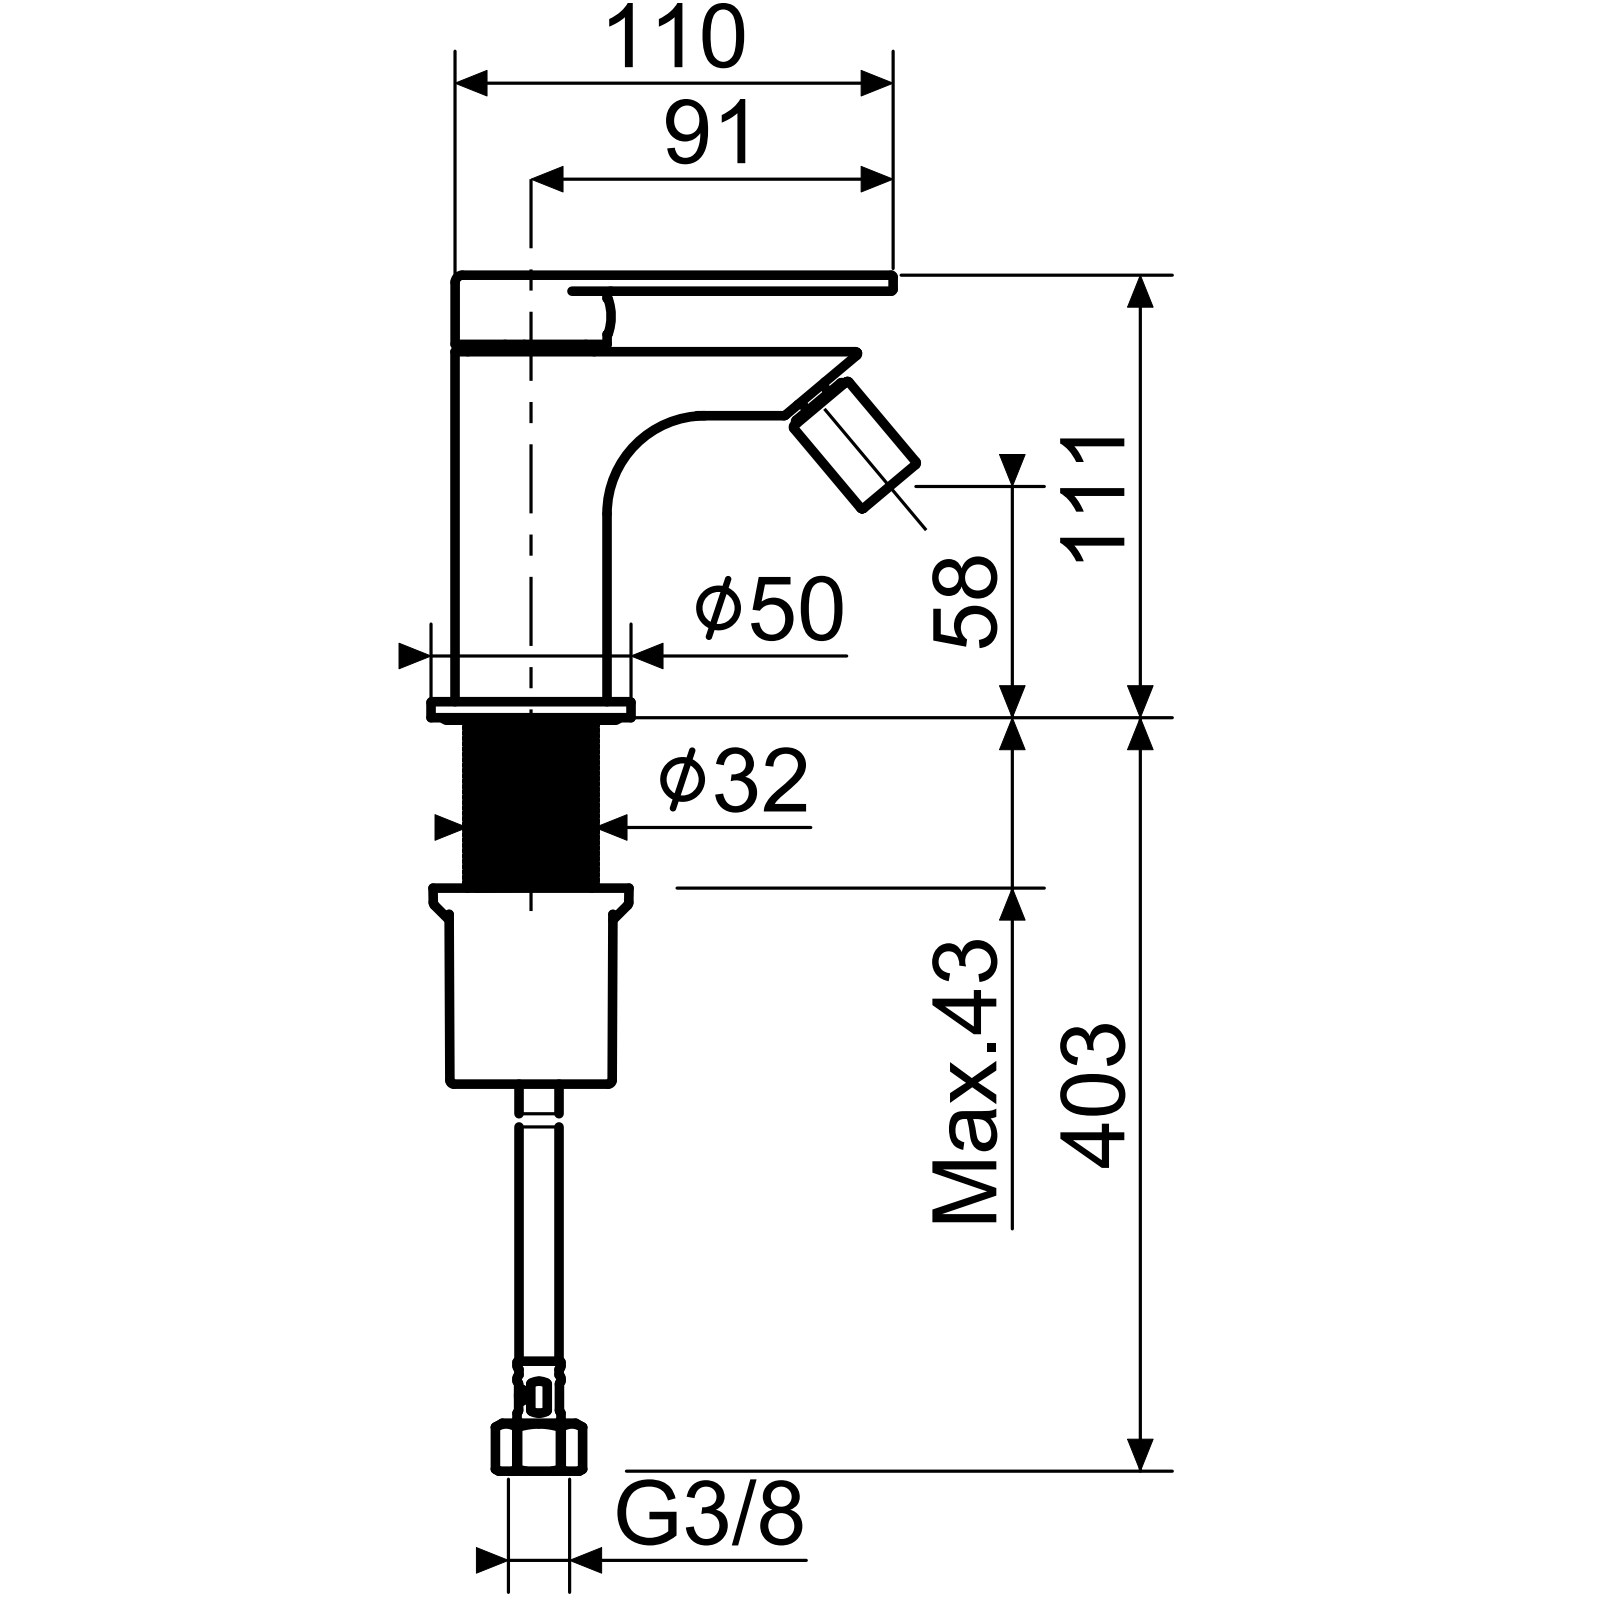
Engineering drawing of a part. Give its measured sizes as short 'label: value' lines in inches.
name: AOTT301C001; AOTT005C001; SPLMAC0001; SCCMAC0001 (+4 more)
written by: CREO PARAMETRIC BY PTC INC, 2020281 (CONFIG_CONTROL_DESIGN)
unit: in
bodies: 7 solids, 2525 faces (1192 planar, 668 cylindrical, 665 other)
size: 6.142 × 5.438 × 2.572
volume: 4.832 in³; area: 91.15 in²
holes: 2× ⌀0.512, 2× ⌀0.512, 1× ⌀0.165, 1× ⌀0.177, 1× ⌀0.197, 1× ⌀0.264, 1× ⌀0.315, 1× ⌀0.402, 1× ⌀0.559, 1× ⌀0.591, 1× ⌀0.63, 1× ⌀0.65
bosses: 2× ⌀1.496, 2× ⌀0.472, 1× ⌀1.969, 1× ⌀1.575, 1× ⌀1.26, 1× ⌀1.244, 1× ⌀1.205, 1× ⌀0.709
rounds: 51× R0.02, 24× R0.005, 16× R0.004, 15× R0.039, 8× R3.808, 8× R4.232, 8× R4.711, 8× R5.468
face distances: 0.157, 0.118, 4.198, 0.753, 0.596, 3.445, 4.041, 0.63, 3.327, 0.714
hole spacings: 0.354, 0.356
